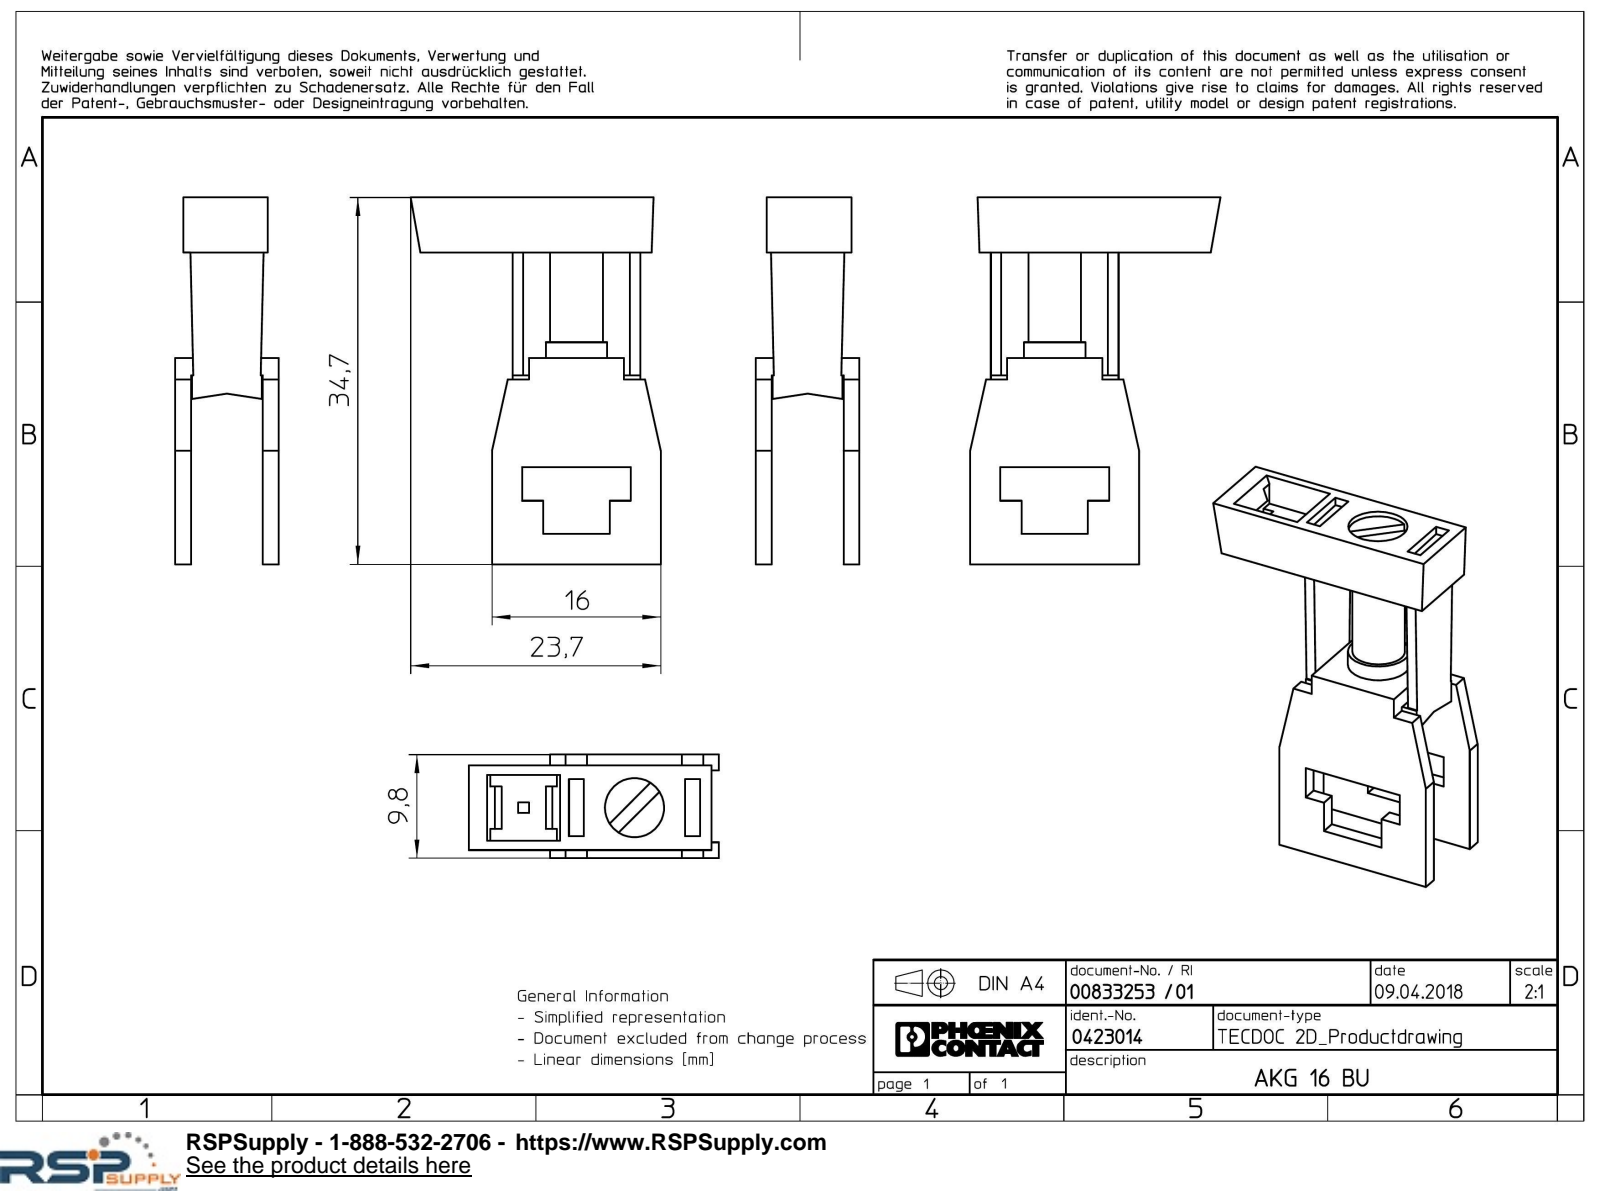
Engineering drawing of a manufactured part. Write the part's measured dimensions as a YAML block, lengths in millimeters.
part_name: "AKG_16_BU-select"
step_written_by: "Creo Elements/Direct Modeling 20.1A 29-Sep-2018 (C) Parametric Technology GmbH (AUTOMOTIVE_DESIGN)"
units: millimeters
bodies: {solids: 1, faces: 104, planar: 98, cylindrical: 6, other: 0}
overall_size: [34.7, 23.7, 9.8]
volume: 2087
surface_area: 2775
round_holes:
  - {diameter: 5.6, count: 1}
round_bosses_or_shafts:
  - {diameter: 5.8, count: 1}
  - {diameter: 5, count: 1}
face_to_face_distances: [8.3, 1.5, 9.8, 6.8, 1, 11.1, 0.46, 0.74, 1.04, 9.04]
